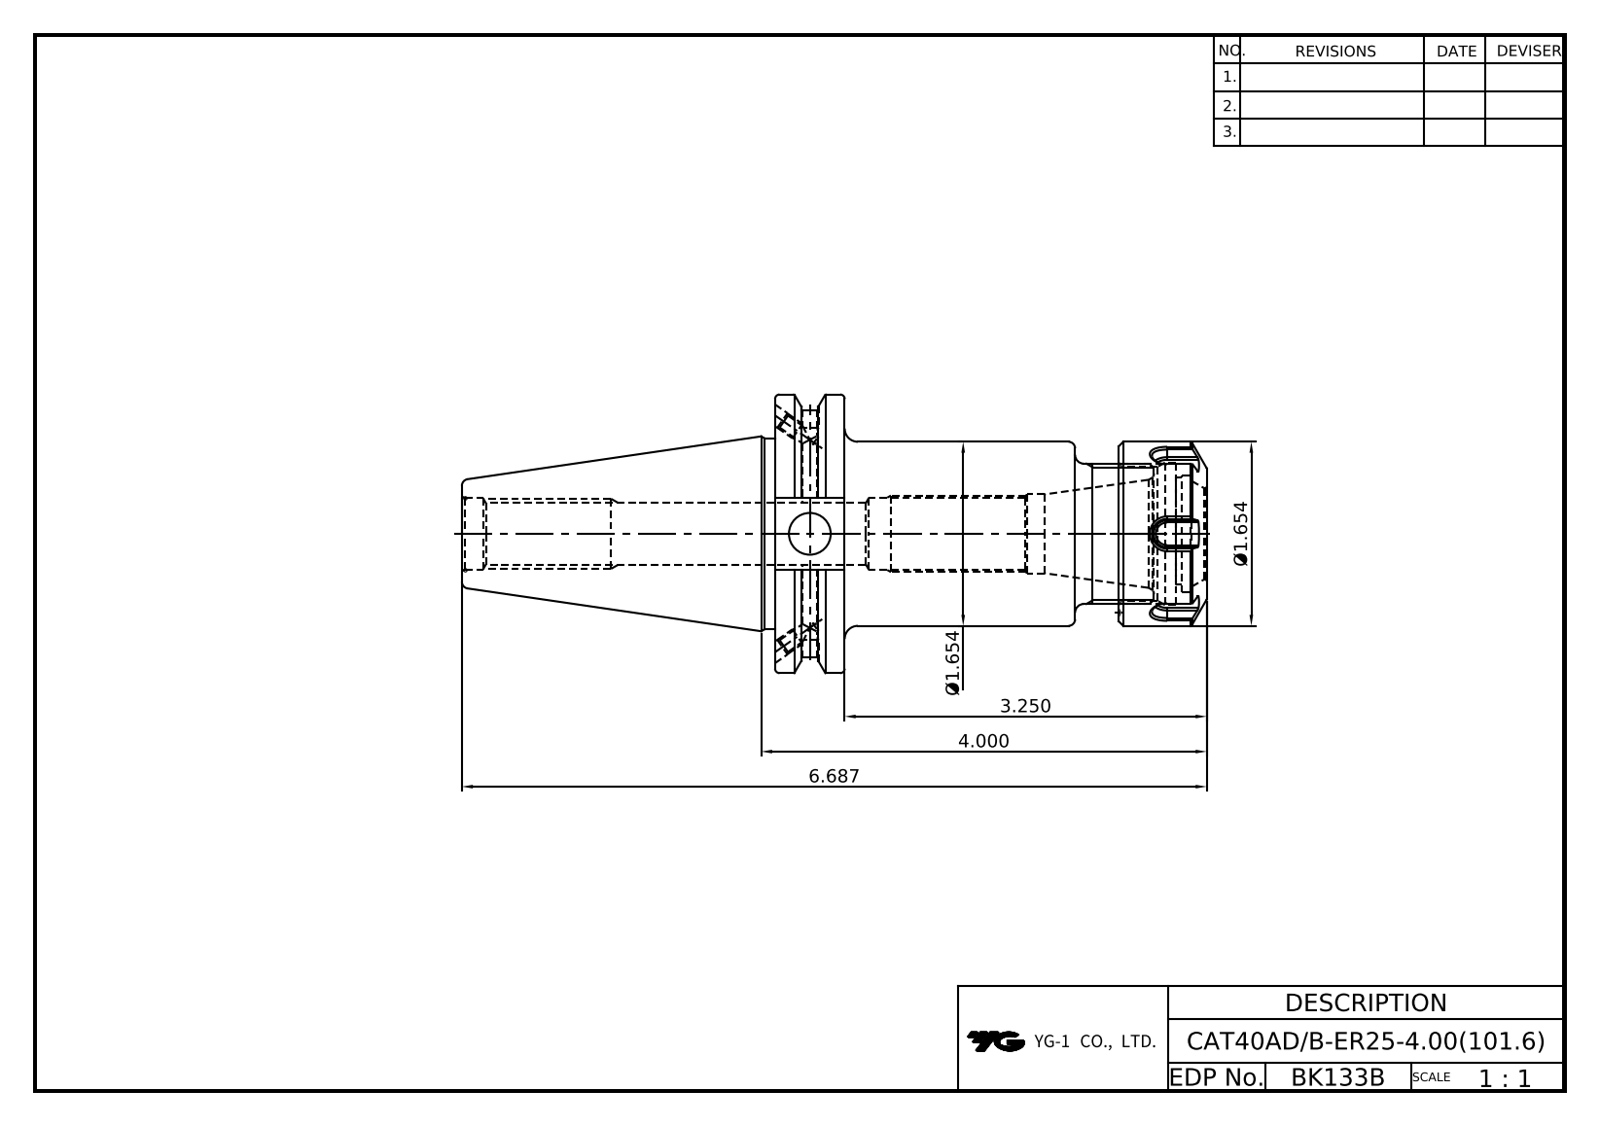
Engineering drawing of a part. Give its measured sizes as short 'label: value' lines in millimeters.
name: LO-CAT40ADB-ER25-4.00; ER25NUT
written by: Autodesk Inventor 2024 (AUTOMOTIVE_DESIGN)
unit: mm
bodies: 2 solids, 170 faces (73 planar, 46 cylindrical, 51 other)
size: 169.85 × 63.5 × 61.09
volume: 182 384 mm³; area: 39 394 mm²
holes: 4× ⌀3.24, 2× ⌀4, 2× ⌀4.2, 1× ⌀9.53, 1× ⌀13.39, 1× ⌀15.75, 1× ⌀16.3, 1× ⌀18, 1× ⌀20.9, 1× ⌀23, 1× ⌀26.8, 1× ⌀30.5
bosses: 1× ⌀63.5, 1× ⌀43.6, 1× ⌀42, 1× ⌀32
rounds: 12× R0.5, 1× R28.15
face distances: 15.88, 78.43, 62.55, 91.33, 75.45, 12.9, 98.43, 82.55, 20, 7.1
